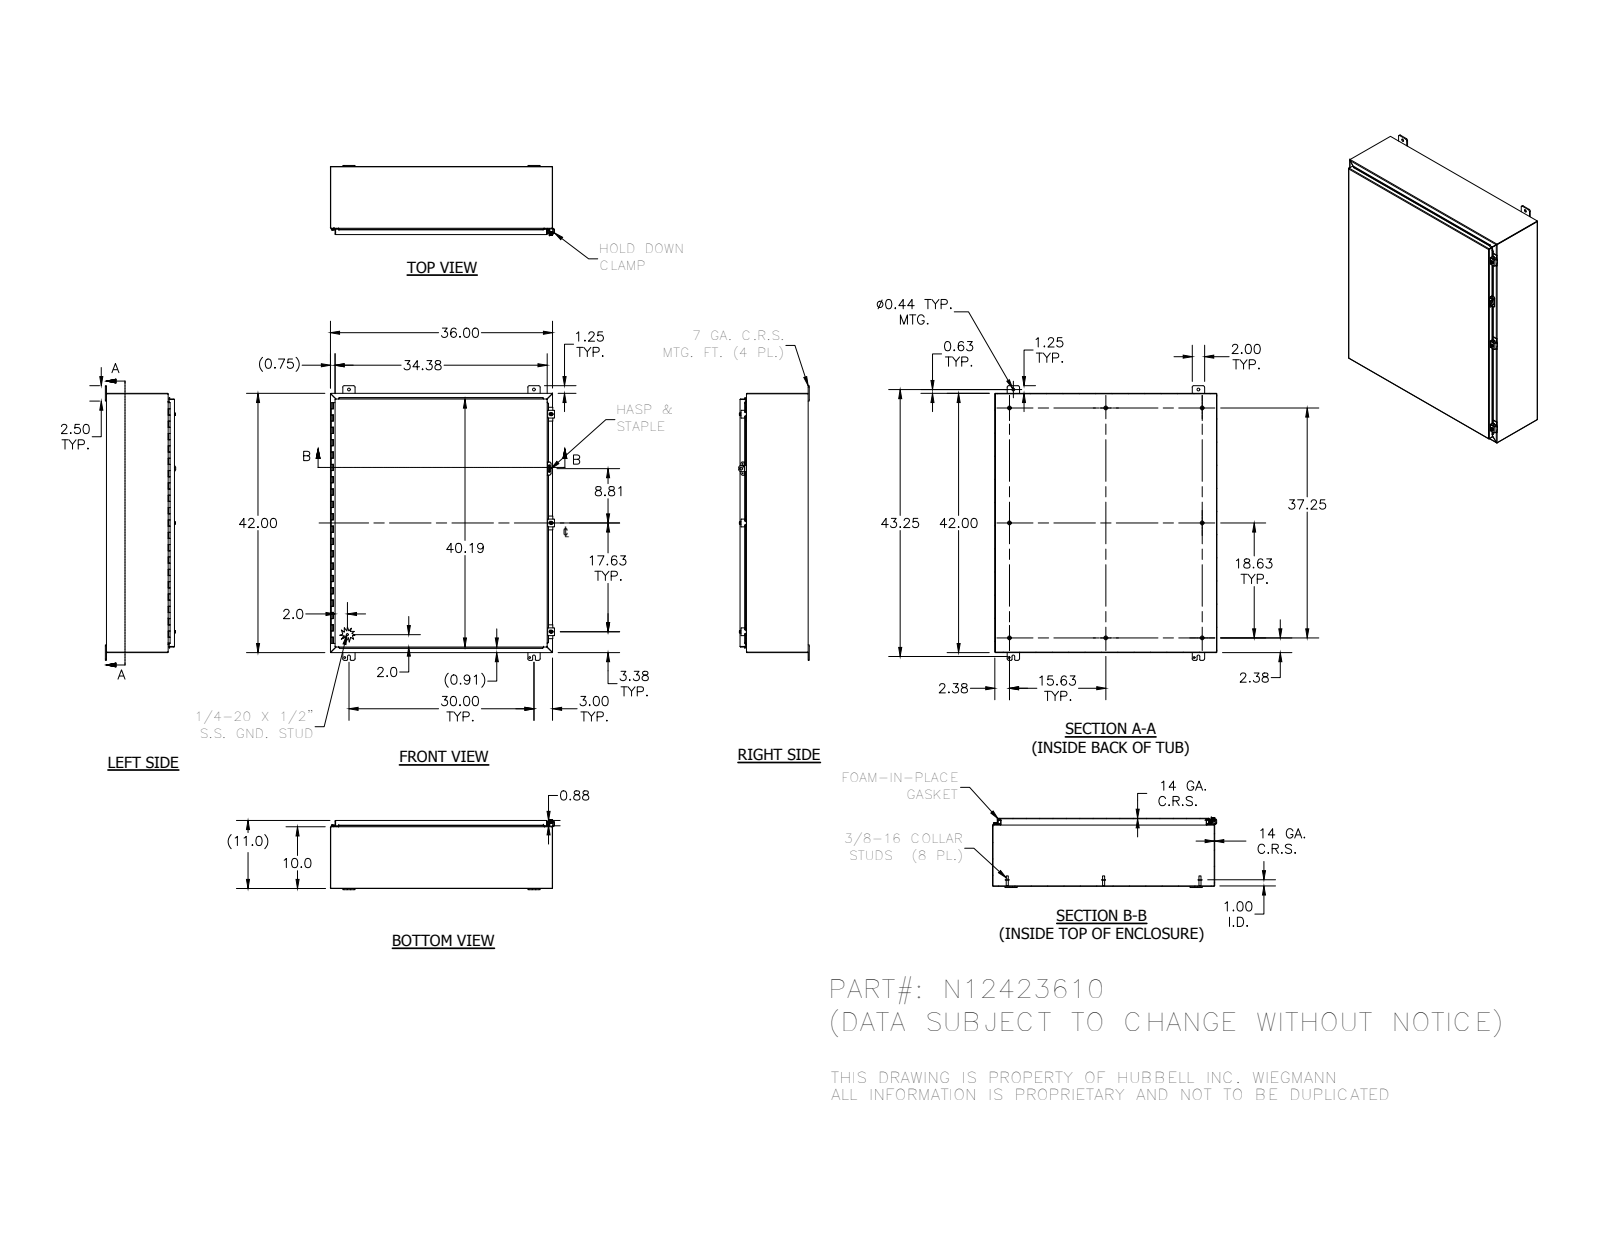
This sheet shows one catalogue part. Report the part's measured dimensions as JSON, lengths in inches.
{"part_name": "N12423610; 34840; 38413; N123610TB (+8 more)", "step_written_by": "Autodesk Inventor 2012 (AUTOMOTIVE_DESIGN)", "units": "inches", "bodies": {"solids": 38, "faces": 1161, "planar": 679, "cylindrical": 357, "other": 125}, "overall_size": [44.5, 36.311, 11.41], "volume_in3": 390.5, "surface_area_in2": 10327, "round_holes": [[0.313, 4], [0.438, 4], [0.11, 3], [0.211, 3], [0.281, 3], [0.3, 3], [0.125, 1], [0.156, 1], [0.5, 1]], "round_bosses_or_shafts": [[0.625, 8], [0.33, 8], [0.25, 5], [0.52, 3], [0.5, 3], [0.35, 3], [0.115, 2], [0.337, 1]], "partial_cylinders_radius": [[0.03, 39], [0.125, 27], [0.25, 27], [0.031, 21], [0.105, 21], [0.063, 15], [0.1, 6], [0.141, 6]], "face_to_face_distances": [0.074, 10.959, 10.885, 11.033, 35.926, 41.926, 35.852, 36, 9.926, 1.033], "hole_center_spacings": [1.593, 30, 42, 51.614, 0.791, 8.838, 29.348, 30.72]}
